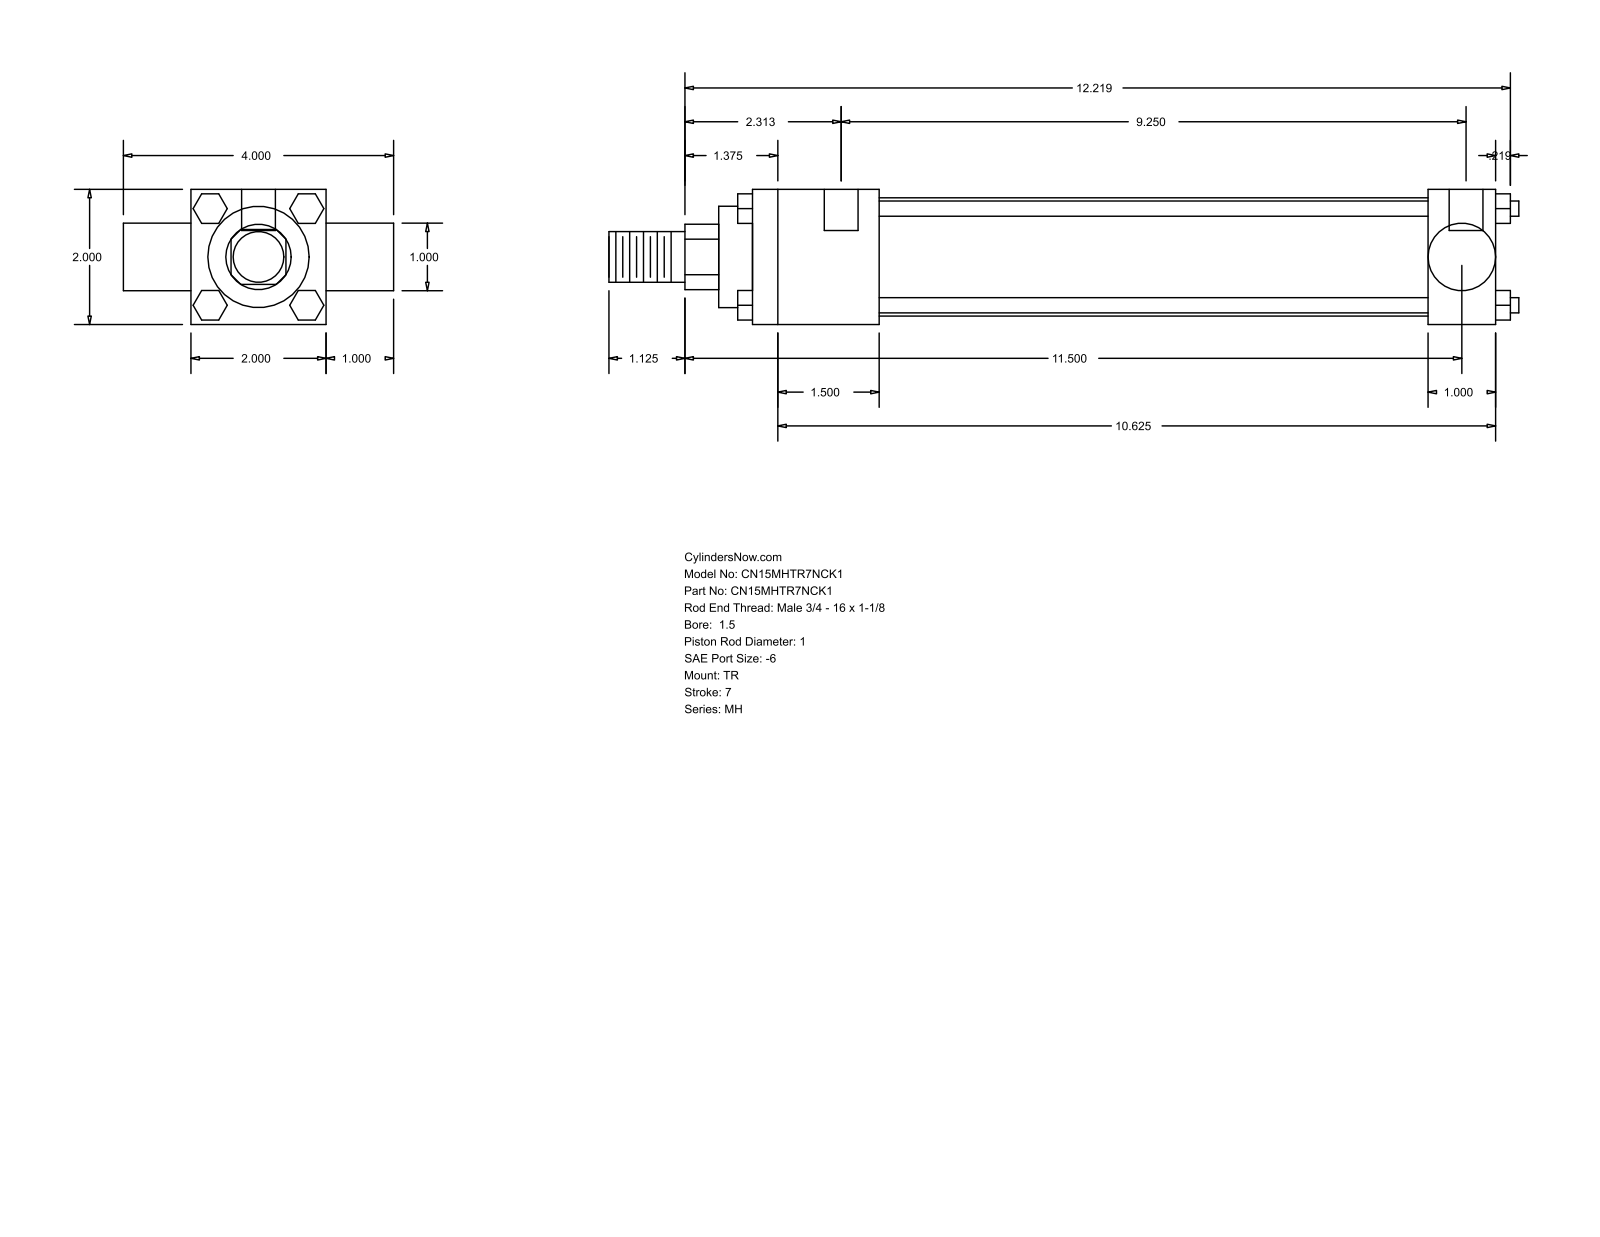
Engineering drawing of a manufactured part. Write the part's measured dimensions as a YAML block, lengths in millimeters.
part_name: "MH_TR__0150_1"
step_written_by: "GSSL Pune (CONFIG_CONTROL_DESIGN)"
units: millimeters
bodies: {solids: 0, faces: 120, planar: 92, cylindrical: 28, other: 0}
overall_size: [342.11, 101.6, 50.8]
round_holes:
  - {diameter: 5.56, count: 3}
  - {diameter: 12.7, count: 2}
round_bosses_or_shafts:
  - {diameter: 5.71, count: 4}
  - {diameter: 44.45, count: 1}
  - {diameter: 38.1, count: 1}
  - {diameter: 25.4, count: 1}
  - {diameter: 25.35, count: 1}
  - {diameter: 19.05, count: 1}
partial_cylinders:
  - {radius: 12.29, count: 1}
face_to_face_distances: [50.8, 25.4, 279.4, 76.2, 47.63, 231.77, 254, 206.37, 101.6, 12.7]
hole_center_spacings: [3.18, 234.95, 238.13]
